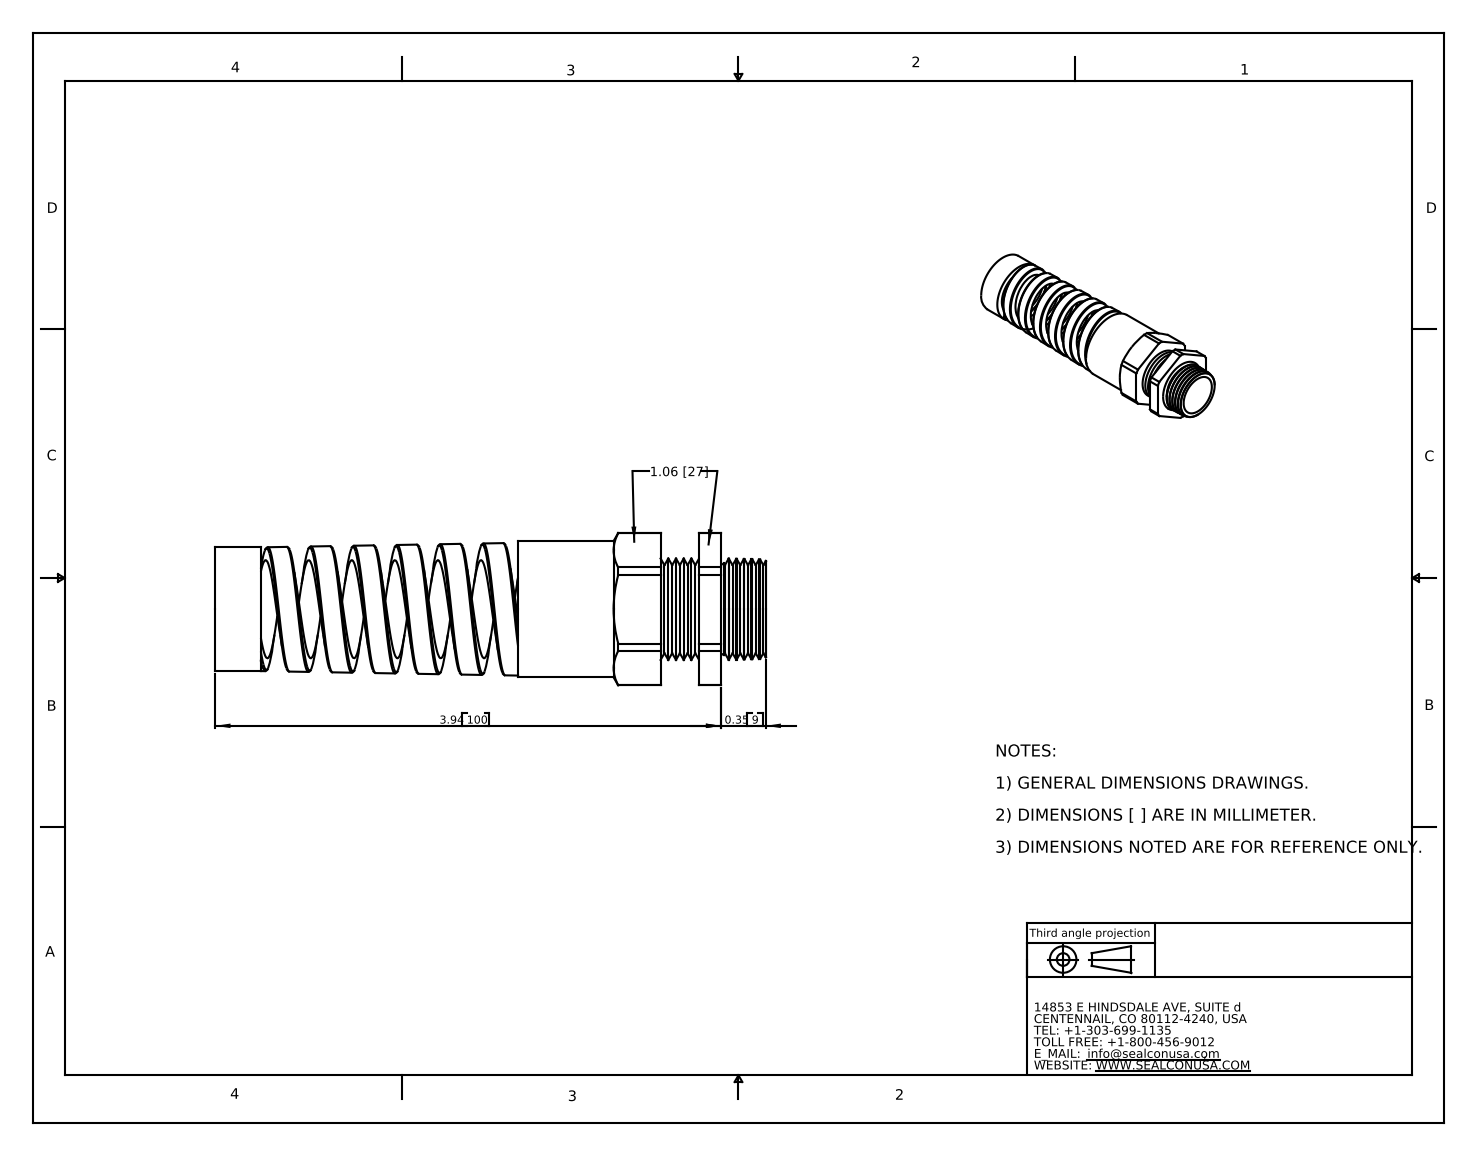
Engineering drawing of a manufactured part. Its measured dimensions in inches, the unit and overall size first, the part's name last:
Units: inches
Overall size (bounding box): 4.29 × 1.187 × 1.06
Round holes (diameter × count): ⌀0.55 ×1, ⌀0.764 ×1, ⌀0.79 ×1
Round bosses / shafts (diameter × count): ⌀1.06 ×1, ⌀0.964 ×1
Partial cylindrical surfaces — rounded edges, fillets, slot ends (radius × count): R0.594 ×1
Main face-to-face distances: 1.06, 0.297, 1.111, 1.407, 1.581, 0.471, 0.174, 2.359, 3.469, 3.766
Volume: 1.406 in³ · Surface area: 24.95 in²
Bodies: 1 solid, 139 faces (19 planar, 34 cylindrical, 86 other)
Part name (STEP PRODUCT): CF22MA
STEP written by: SolidWorks 2007 (CONFIG_CONTROL_DESIGN)
